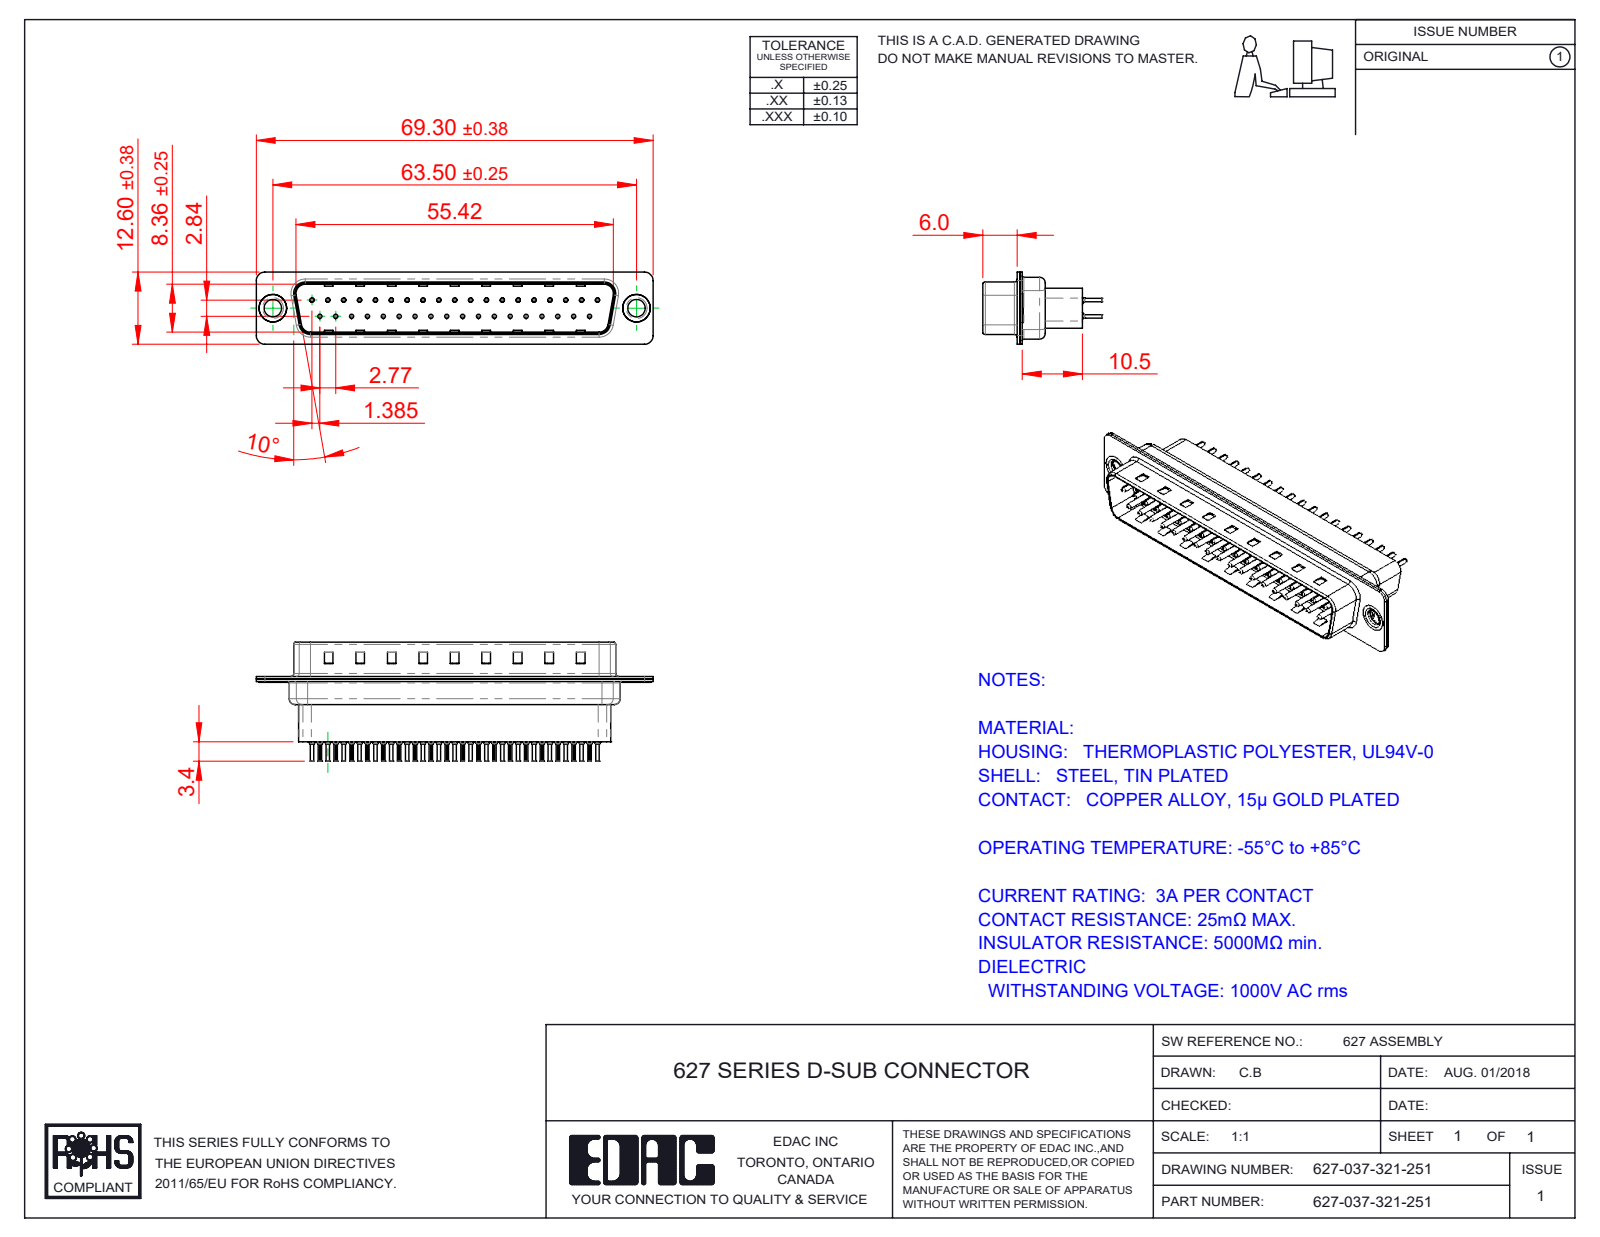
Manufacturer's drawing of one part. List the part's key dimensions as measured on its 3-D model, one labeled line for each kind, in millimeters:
Part name (STEP PRODUCT): 627 Thru Hole Rivet; 627 Shell Rear_37 Contacts; 627 Contact Row 1_21H; 627-037-321-051 (+3 more)
STEP written by: SolidWorks 2020 (CONFIG_CONTROL_DESIGN)
Units: millimetres
Bodies: 42 solids, 4012 faces (1091 planar, 1494 cylindrical, 1427 other)
Overall size (bounding box): 69.3 × 20.8 × 12.6
Volume: 5 229 mm³ · Surface area: 13 415 mm²
Round holes (diameter × count): ⌀0.2 ×37, ⌀0.35 ×37, ⌀1.1 ×37, ⌀1.6 ×37, ⌀3.05 ×2, ⌀4 ×2, ⌀4.8 ×2
Round bosses / shafts (diameter × count): ⌀2 ×37, ⌀1.5 ×37, ⌀0.75 ×37, ⌀0.6 ×37, ⌀5 ×2, ⌀4.9 ×2, ⌀3.55 ×2
Partial cylindrical surfaces — rounded edges, fillets, slot ends (radius × count): R0.1 ×74, R1.5 ×16, R2 ×12, R0.5 ×8, R1.6 ×8, R0.25 ×4, R0.6 ×4, R0.65 ×4
Main face-to-face distances: 0.4, 0.82, 9.58, 0.68, 7.68, 0.45, 1.5, 1.08, 8.08, 8.76
Hole centre spacings: 3.16, 2.77, 5.54, 8.31, 5.04, 10.1, 11.08, 12.78
